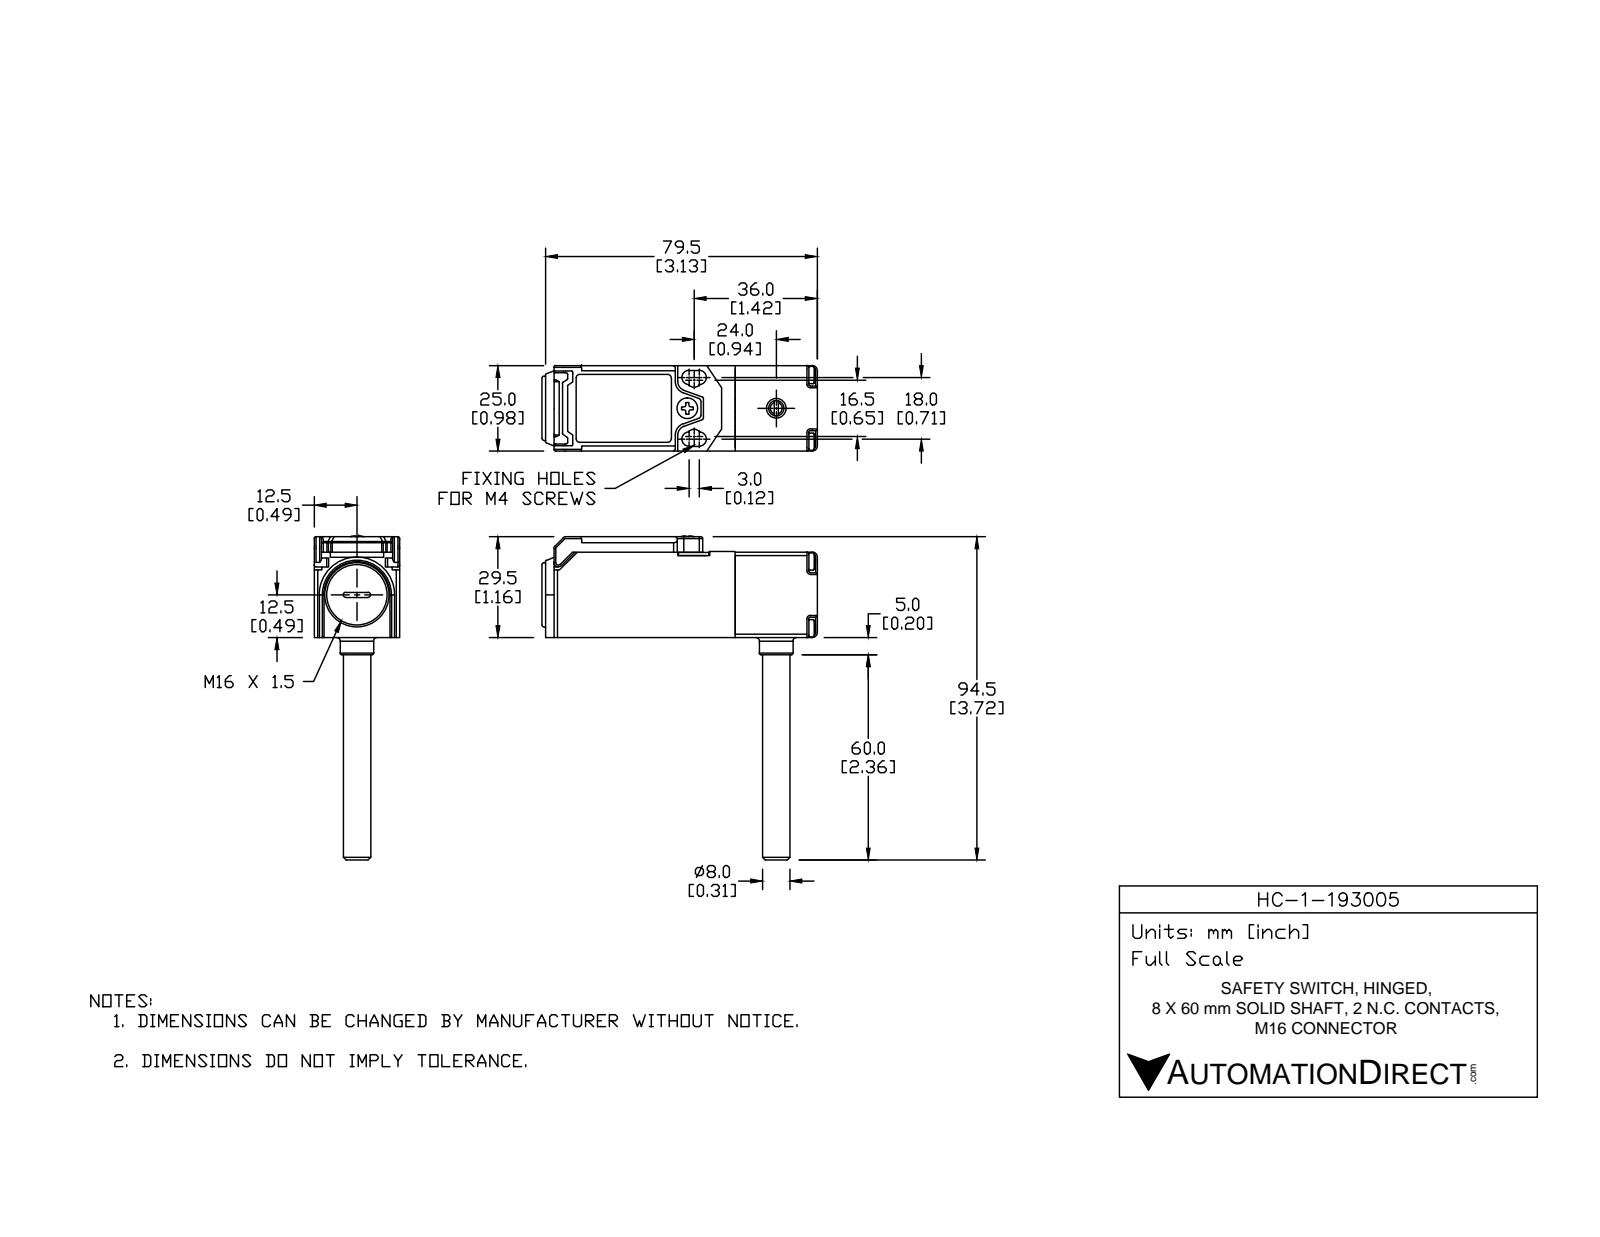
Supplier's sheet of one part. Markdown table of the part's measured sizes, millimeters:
| quantity | value |
| --- | --- |
| part name | HC-1-193005 |
| STEP written by | SolidWorks 2014 (AUTOMOTIVE_DESIGN) |
| units | millimeters |
| bodies | 14 solids, 1702 faces (700 planar, 601 cylindrical, 401 other) |
| overall size | 94.7 × 80.5 × 25 |
| volume | 28 400 mm³ |
| surface area | 27 650 mm² |
| round holes (diameter × count) | 3.2 × 5, 2.4 × 4, 1.5 × 2, 1.6 × 2, 1.8 × 2, 2.2 × 2, 3.6 × 2, 1.4 × 1, 2.1 × 1, 2.5 × 1, 2.6 × 1, 4.7 × 1 |
| round bosses / shafts (diameter × count) | 2.6 × 5, 5 × 4, 2 × 4, 3.5 × 2, 18.8 × 1, 13.5 × 1, 9.8 × 1, 8 × 1 |
| partial cylindrical surfaces (radius × count) | 0.5 × 226, 0.1 × 24, 0.3 × 20, 1 × 20, 1.5 × 7, 2.1 × 6, 2.8 × 6, 0.2 × 4 |
| main face-to-face distances | 25, 2, 1.8, 23.2, 1, 23, 24, 21, 22.2, 29.2 |
| hole center spacings | 13.8, 19.5, 4.3, 4.7, 6.2, 10.5, 10.7, 10.8 |
